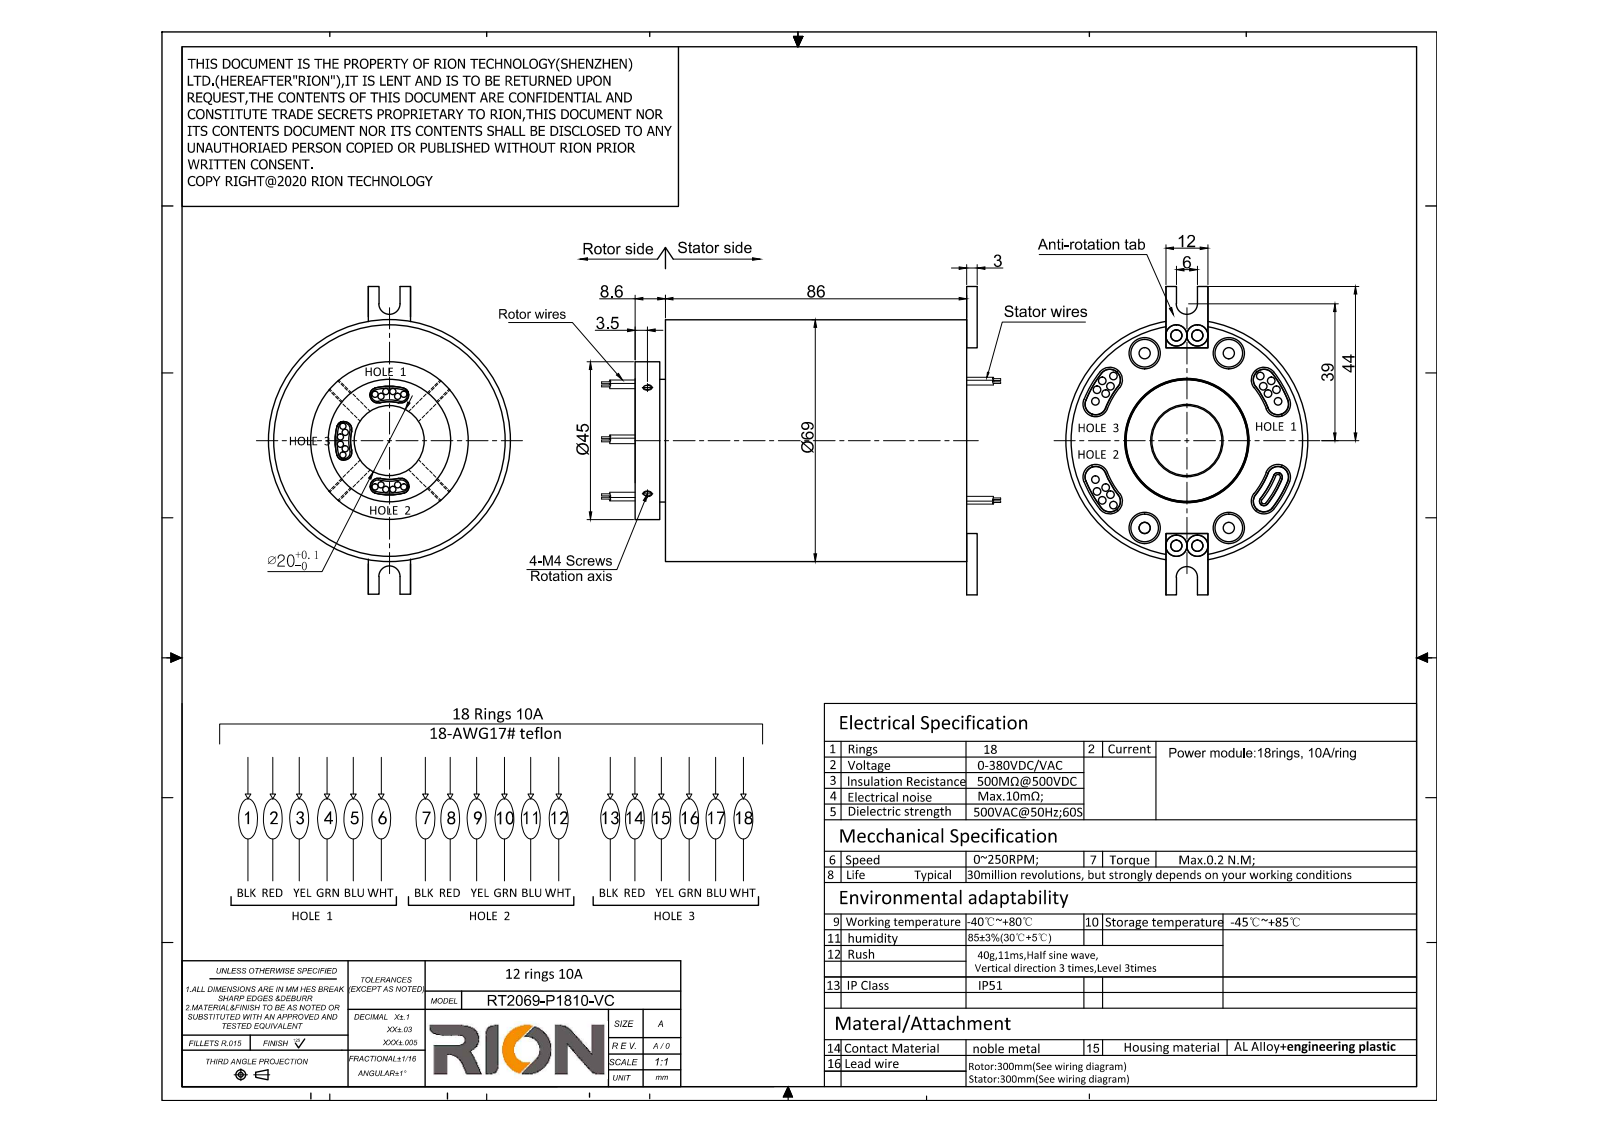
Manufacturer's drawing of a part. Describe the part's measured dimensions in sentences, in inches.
The part is named "MT2069-P1810". Its 3-D file was written by "SolidWorks 2014 (CONFIG_CONTROL_DESIGN)". It is 1 solid with 244 faces: 83 planar, 145 cylindrical and 16 other. Overall it measures 4.827 by 3.465 by 2.717 inches. Its volume is 18.64 cubic inches and its surface area 64.81 square inches. Round holes: 4 of diameter 0.098, 4 of diameter 0.126, 2 of diameter 0.13, 1 of diameter 0.787, 1 of diameter 0.913, 1 of diameter 2.598. Round bosses or shafts: 18 of diameter 0.071, 18 of diameter 0.051, 1 of diameter 2.717, 1 of diameter 2.591, 1 of diameter 1.772, 1 of diameter 1.378, 1 of diameter 0.906. Partial cylindrical surfaces (rounded edges, fillets, slot ends): 12 of radius 0.079, 2 of radius 0.118, 1 of radius 0.454, 1 of radius 0.612. The main face-to-face distances are 3.386, 3.724, 0.339, 0.276, 3.449, 0.063, 0.118, 3.567, 3.504, 3.843. The hole center spacings are 1.187, 0.236, 2.362, 2.374.
